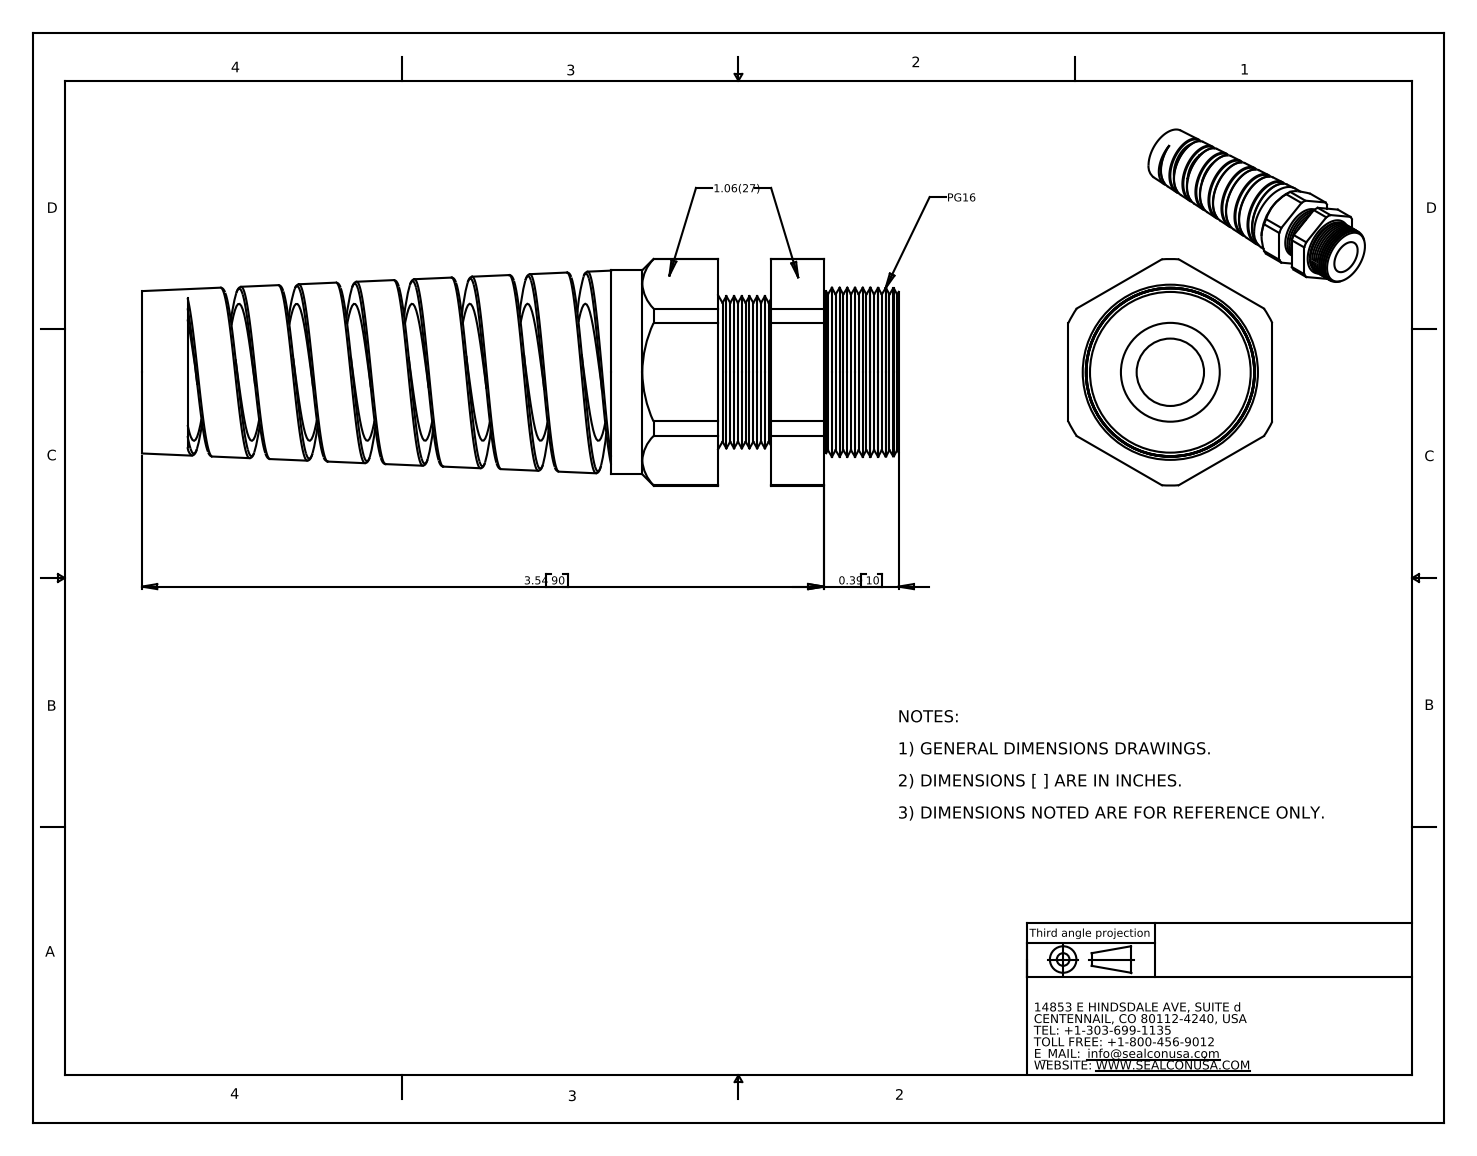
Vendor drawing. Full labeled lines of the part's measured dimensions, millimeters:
Part name (STEP PRODUCT): CF16BR-GY
STEP written by: SolidWorks 2007 (CONFIG_CONTROL_DESIGN)
Units: millimetres
Bodies: 2 solids, 176 faces (24 planar, 39 cylindrical, 113 other)
Overall size (bounding box): 99.8 × 29.9 × 26.9
Volume: 24 220 mm³ · Surface area: 17 750 mm²
Round holes (diameter × count): ⌀8.9 ×1, ⌀18.1 ×1, ⌀20.3 ×1
Round bosses / shafts (diameter × count): ⌀26.9 ×1
Partial cylindrical surfaces — rounded edges, fillets, slot ends (radius × count): R9.3 ×1, R14.9 ×1
Main face-to-face distances: 26.9, 6.9, 23.8, 16.9, 13.9, 7, 9.9, 12.2, 19.2, 26.2
